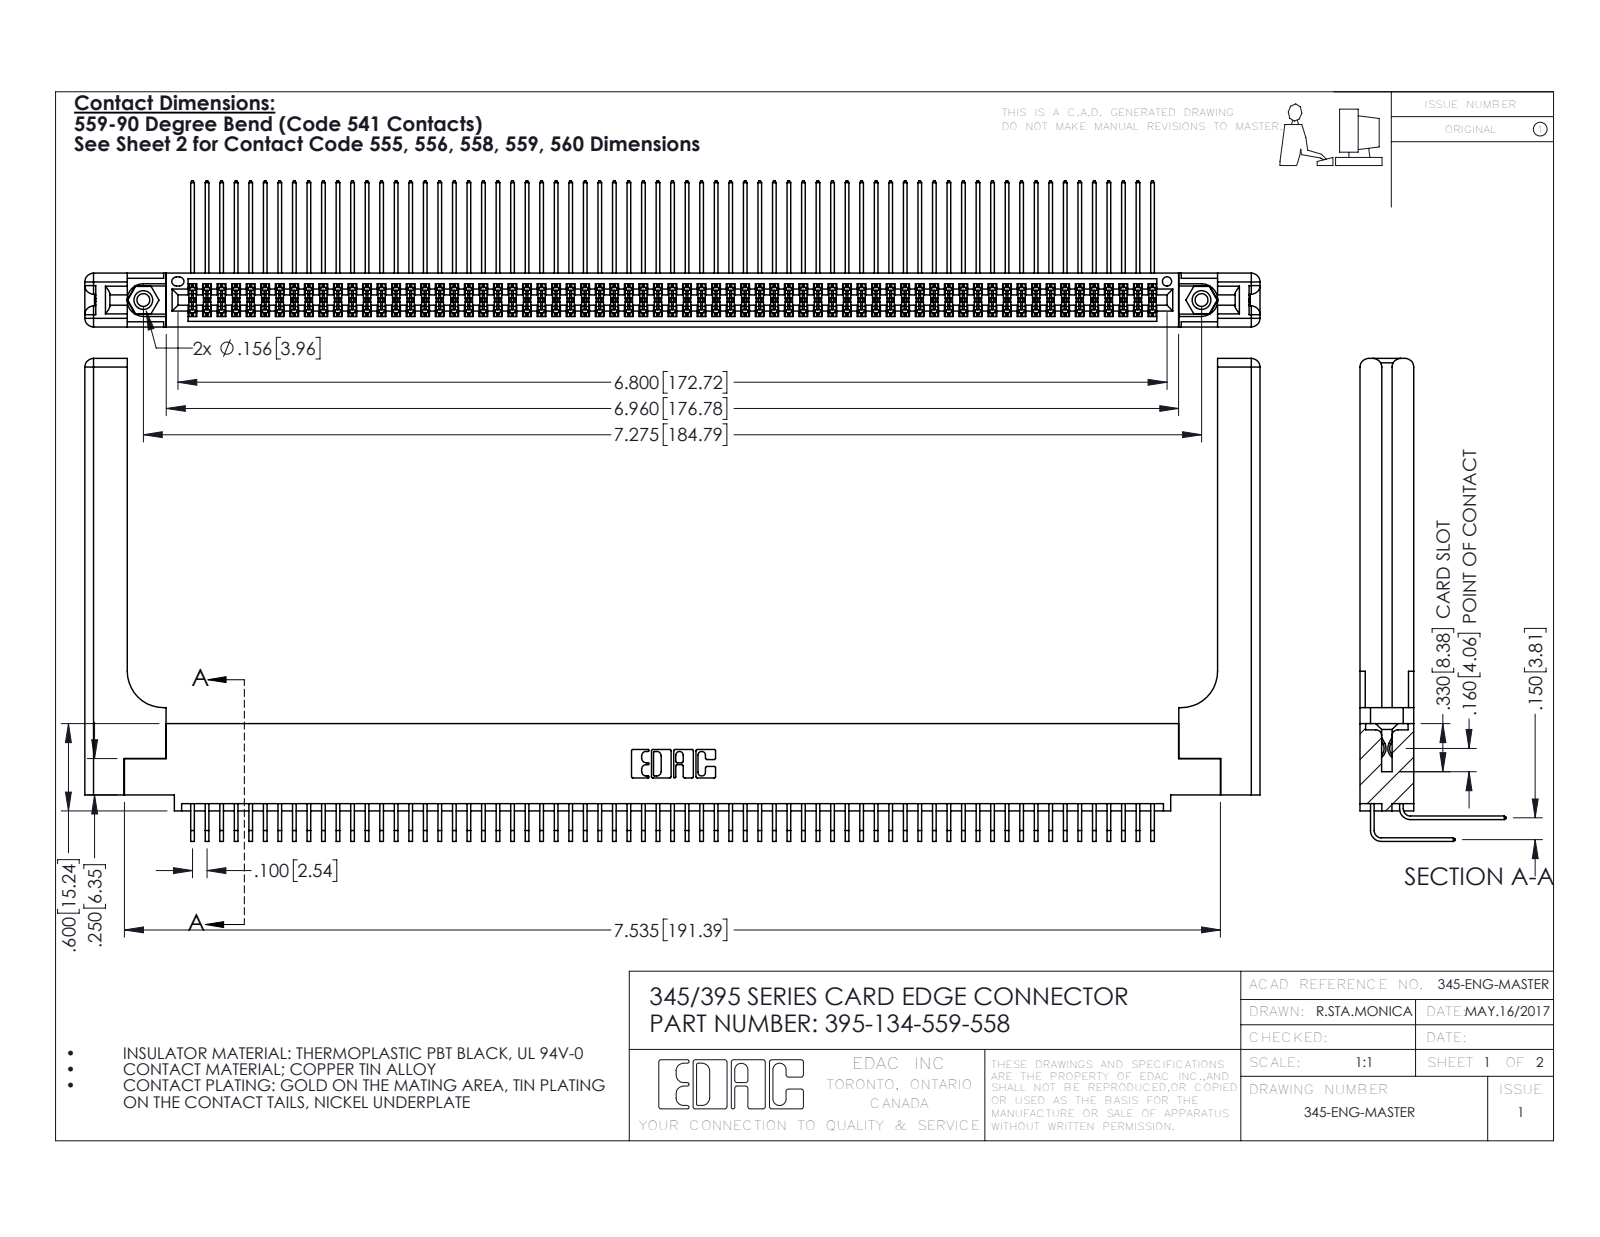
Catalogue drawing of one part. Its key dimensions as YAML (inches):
part_name: "345 Part_0.110 Offset - 0.156 Dia-TH; 345-220-058_345-220-058; 395-134-559-558; 345-292-001_558 559 Tail - 1 (+2 more)"
step_written_by: "SolidWorks 2016 (CONFIG_CONTROL_DESIGN)"
units: inches
bodies: {solids: 139, faces: 7354, planar: 4922, cylindrical: 2372, other: 60}
overall_size: [8.079, 3.319, 1.005]
volume: 1.79
surface_area: 62.18
round_holes:
  - {diameter: 0.089, count: 2}
  - {diameter: 0.125, count: 2}
  - {diameter: 0.156, count: 2}
  - {diameter: 0.064, count: 1}
round_bosses_or_shafts:
  - {diameter: 0.155, count: 2}
partial_cylinders:
  - {radius: 0.006, count: 201}
  - {radius: 0.01, count: 22}
  - {radius: 0.06, count: 16}
  - {radius: 0.007, count: 6}
  - {radius: 0.031, count: 6}
  - {radius: 0.026, count: 3}
  - {radius: 0.014, count: 2}
  - {radius: 0.019, count: 2}
face_to_face_distances: [0.072, 0.298, 0.37, 0.098, 0.272, 0.025, 0.2, 0.225, 0.175, 0.15]
hole_center_spacings: [0.27, 7.039, 7.275]
